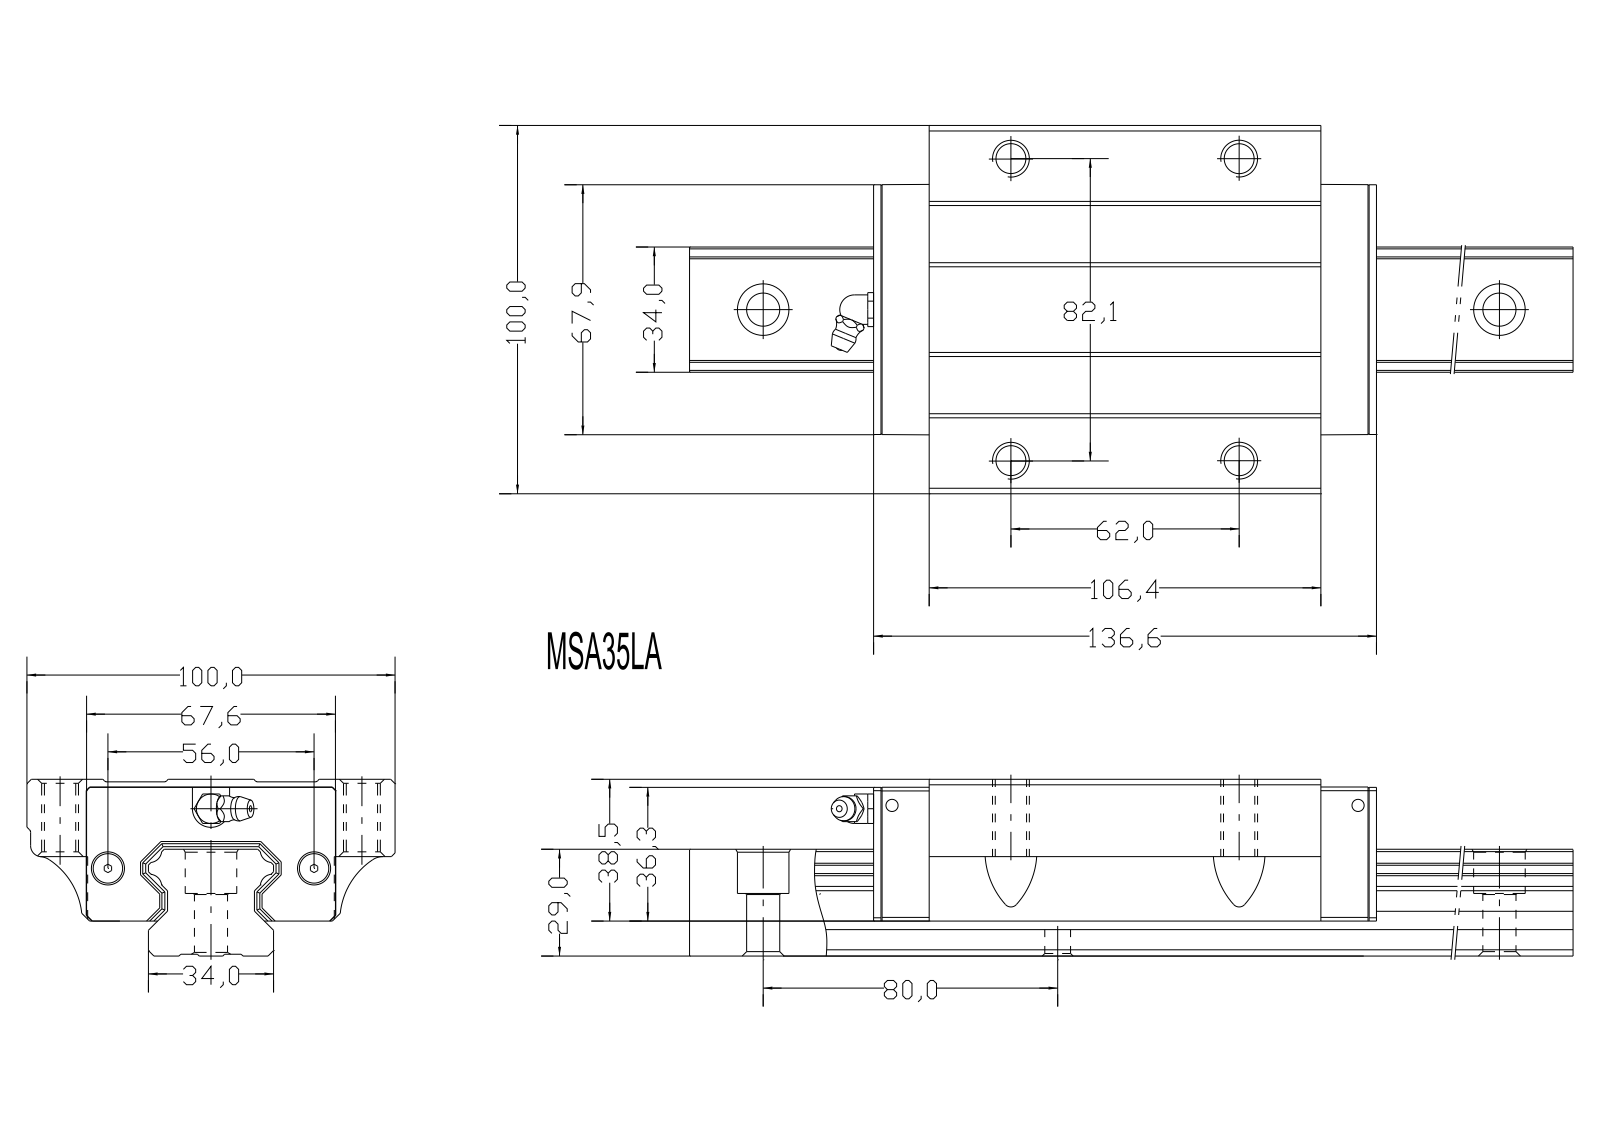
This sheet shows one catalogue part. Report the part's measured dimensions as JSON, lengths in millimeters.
{"step_written_by": "Kubotek KeyCreator V6.5.2 (0407) (CONFIG_CONTROL_DESIGN)", "units": "millimeters", "bodies": {"solids": 3, "faces": 238, "planar": 145, "cylindrical": 76, "other": 17}, "overall_size": [280, 100, 48], "volume_mm3": 574076, "surface_area_mm2": 91439, "round_holes": [[9, 6], [10, 4], [14, 4], [4.5, 2]], "round_bosses_or_shafts": [[8, 1]], "partial_cylinders_radius": [[3.5, 4], [7, 4], [5, 2], [20, 2], [1, 1], [3, 1], [5.05, 1]], "face_to_face_distances": [19, 0.7, 47.3, 48, 29, 9.5, 19.5, 38.5, 16.8, 38.3], "hole_center_spacings": [41.98, 81.99, 97.99, 156.47, 80, 62, 82, 102.8]}
